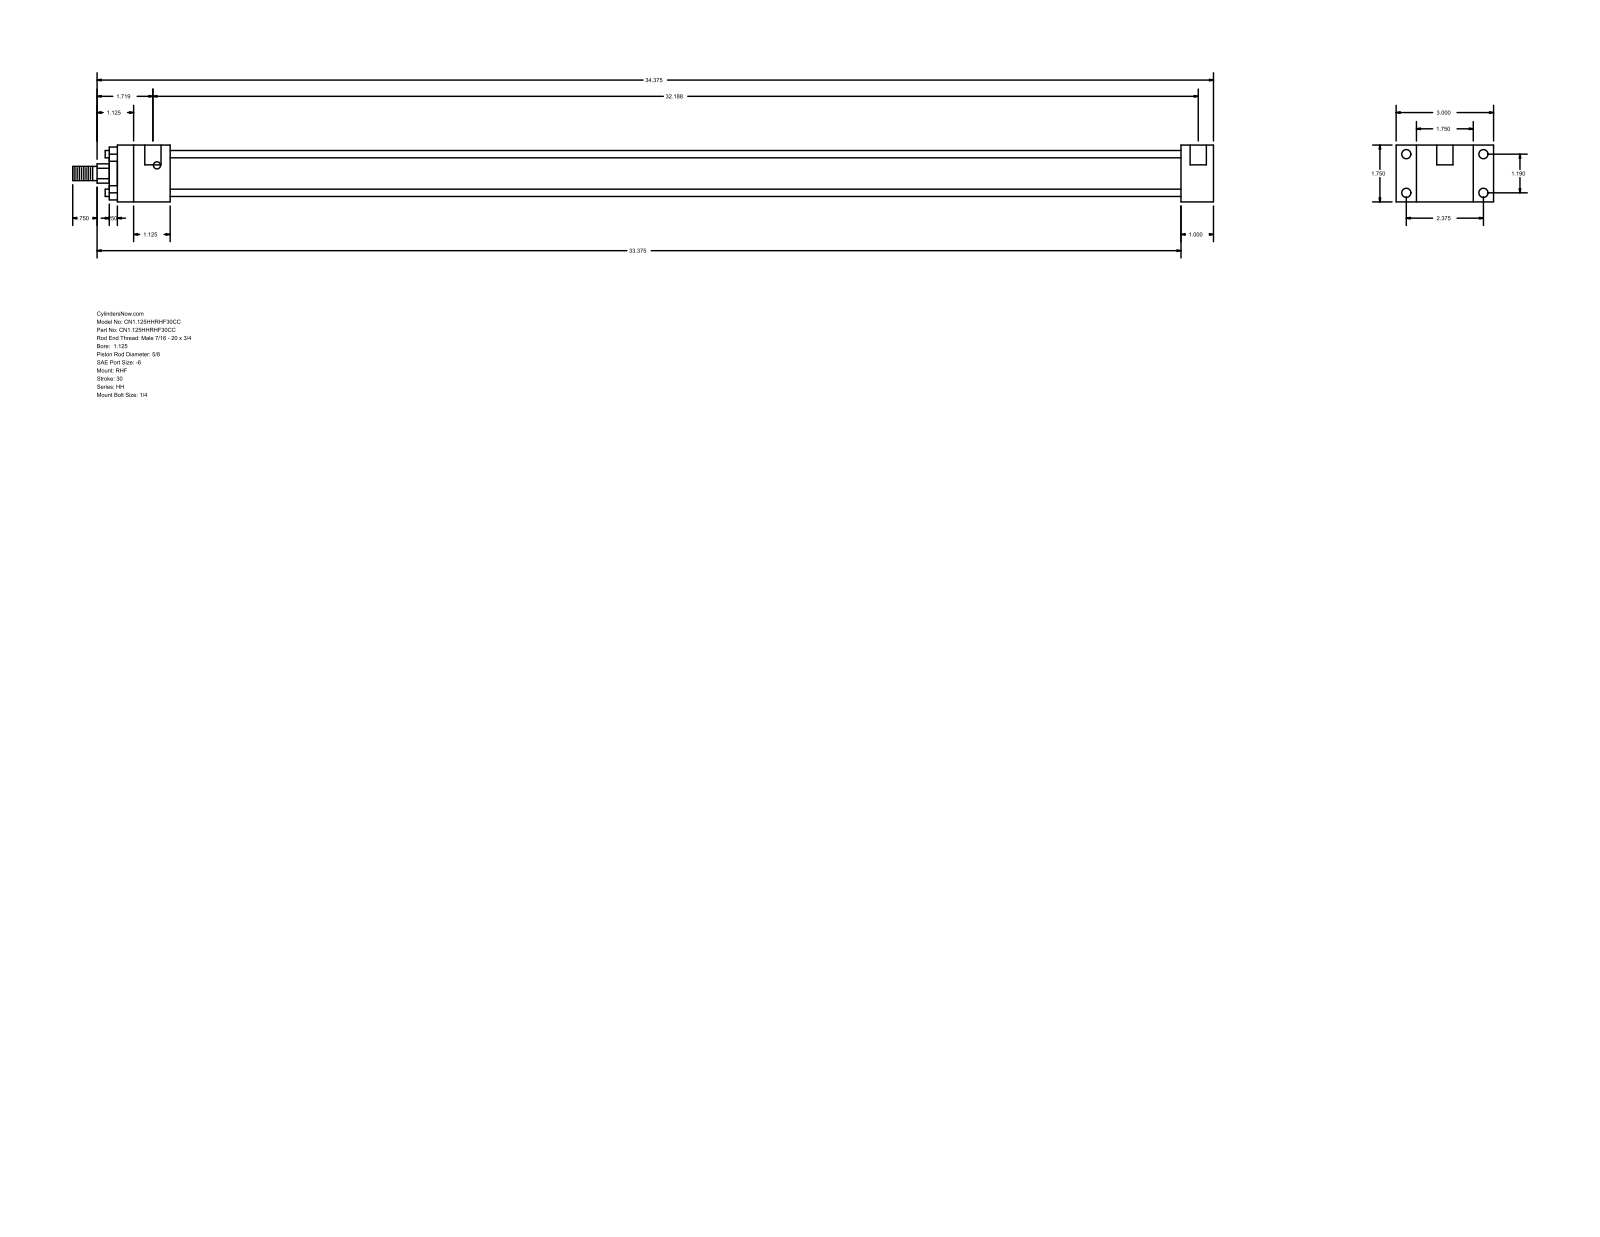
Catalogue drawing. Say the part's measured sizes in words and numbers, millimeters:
The part is named "HH_RHF__0112_0.625". Its 3-D file was written by "GSSL Pune (CONFIG_CONTROL_DESIGN)". It is 0 solids with 88 faces: 60 planar, 28 cylindrical and 0 other. Overall it measures 892.17 by 76.2 by 44.45 millimeters. Round holes: 4 of diameter 5.56, 4 of diameter 7.14, 2 of diameter 12.7. Round bosses or shafts: 4 of diameter 5.71, 1 of diameter 34.92, 1 of diameter 28.57, 1 of diameter 15.88, 1 of diameter 11.11. Partial cylindrical surfaces (rounded edges, fillets, slot ends): 1 of radius 7.54. The main face-to-face distances are 44.46, 15.87, 60.33, 25.39, 76.2, 790.58, 815.97, 41.27, 831.85, 857.24. The hole center spacings are 30.22, 60.32, 67.47, 814.39, 3.17, 817.56.
